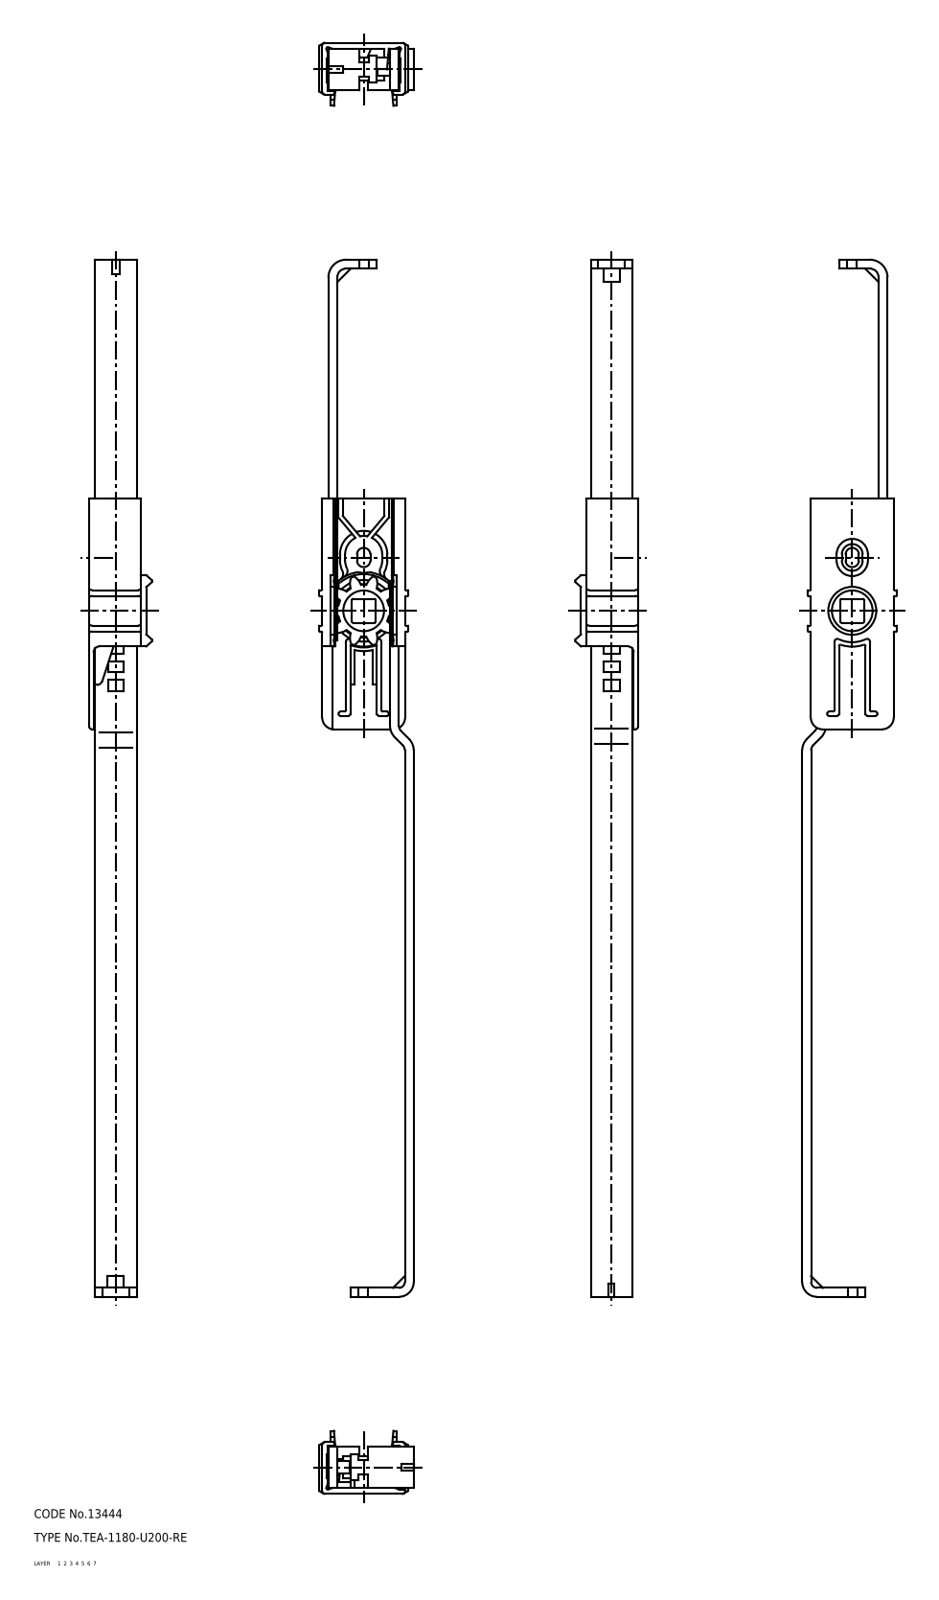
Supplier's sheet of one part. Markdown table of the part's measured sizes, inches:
| quantity | value |
| --- | --- |
| part name | rod_2; rod_1; body_2; body_1 (+1 more) |
| STEP written by | CADfix (AUTOMOTIVE_DESIGN) |
| units | inches |
| bodies | 4 solids, 432 faces (0 planar, 0 cylindrical, 432 other) |
| overall size | 13.78 × 1.256 × 0.839 |
| volume | 1.516 in³ |
| surface area | 38.35 in² |
